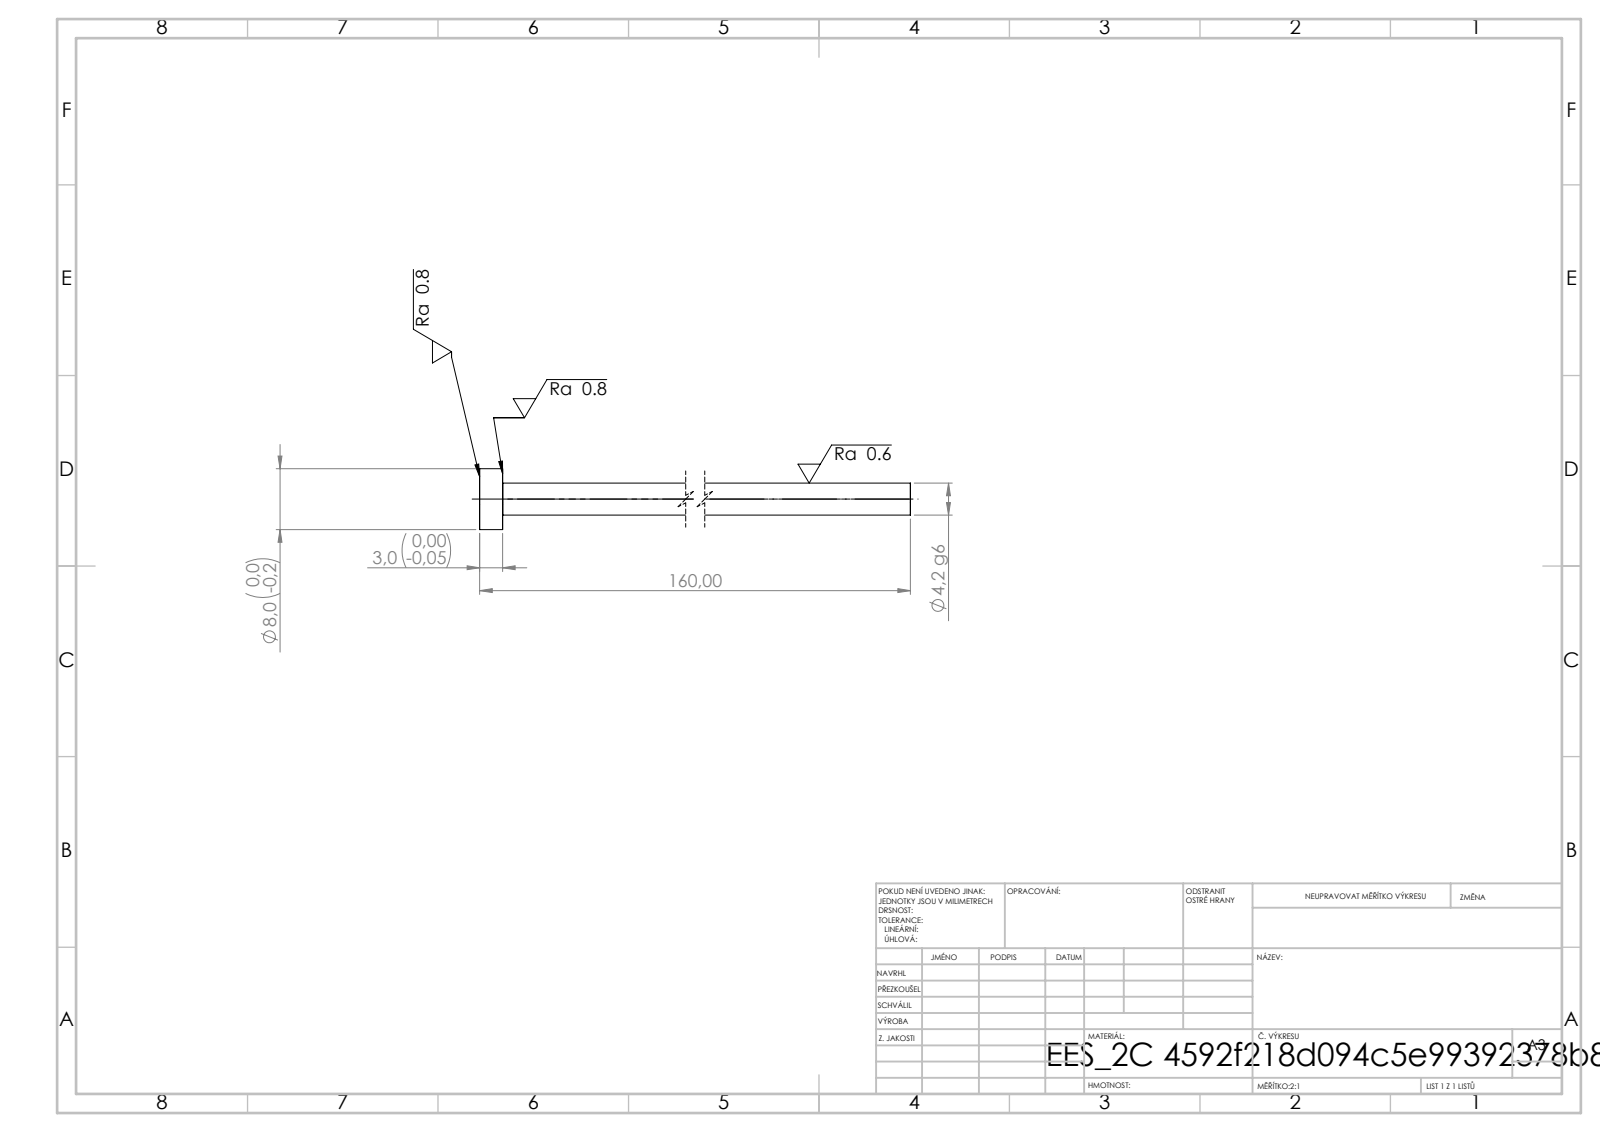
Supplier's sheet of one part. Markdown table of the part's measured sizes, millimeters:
| quantity | value |
| --- | --- |
| STEP written by | SolidWorks 2019 (CONFIG_CONTROL_DESIGN) |
| units | millimeters |
| bodies | 1 solid, 7 faces (3 planar, 4 cylindrical, 0 other) |
| overall size | 160 × 8 × 8 |
| volume | 2 326 mm³ |
| surface area | 2 248 mm² |
| round bosses / shafts (diameter × count) | 8 × 1, 4.2 × 1 |
| main face-to-face distances | 3, 160, 157 |
